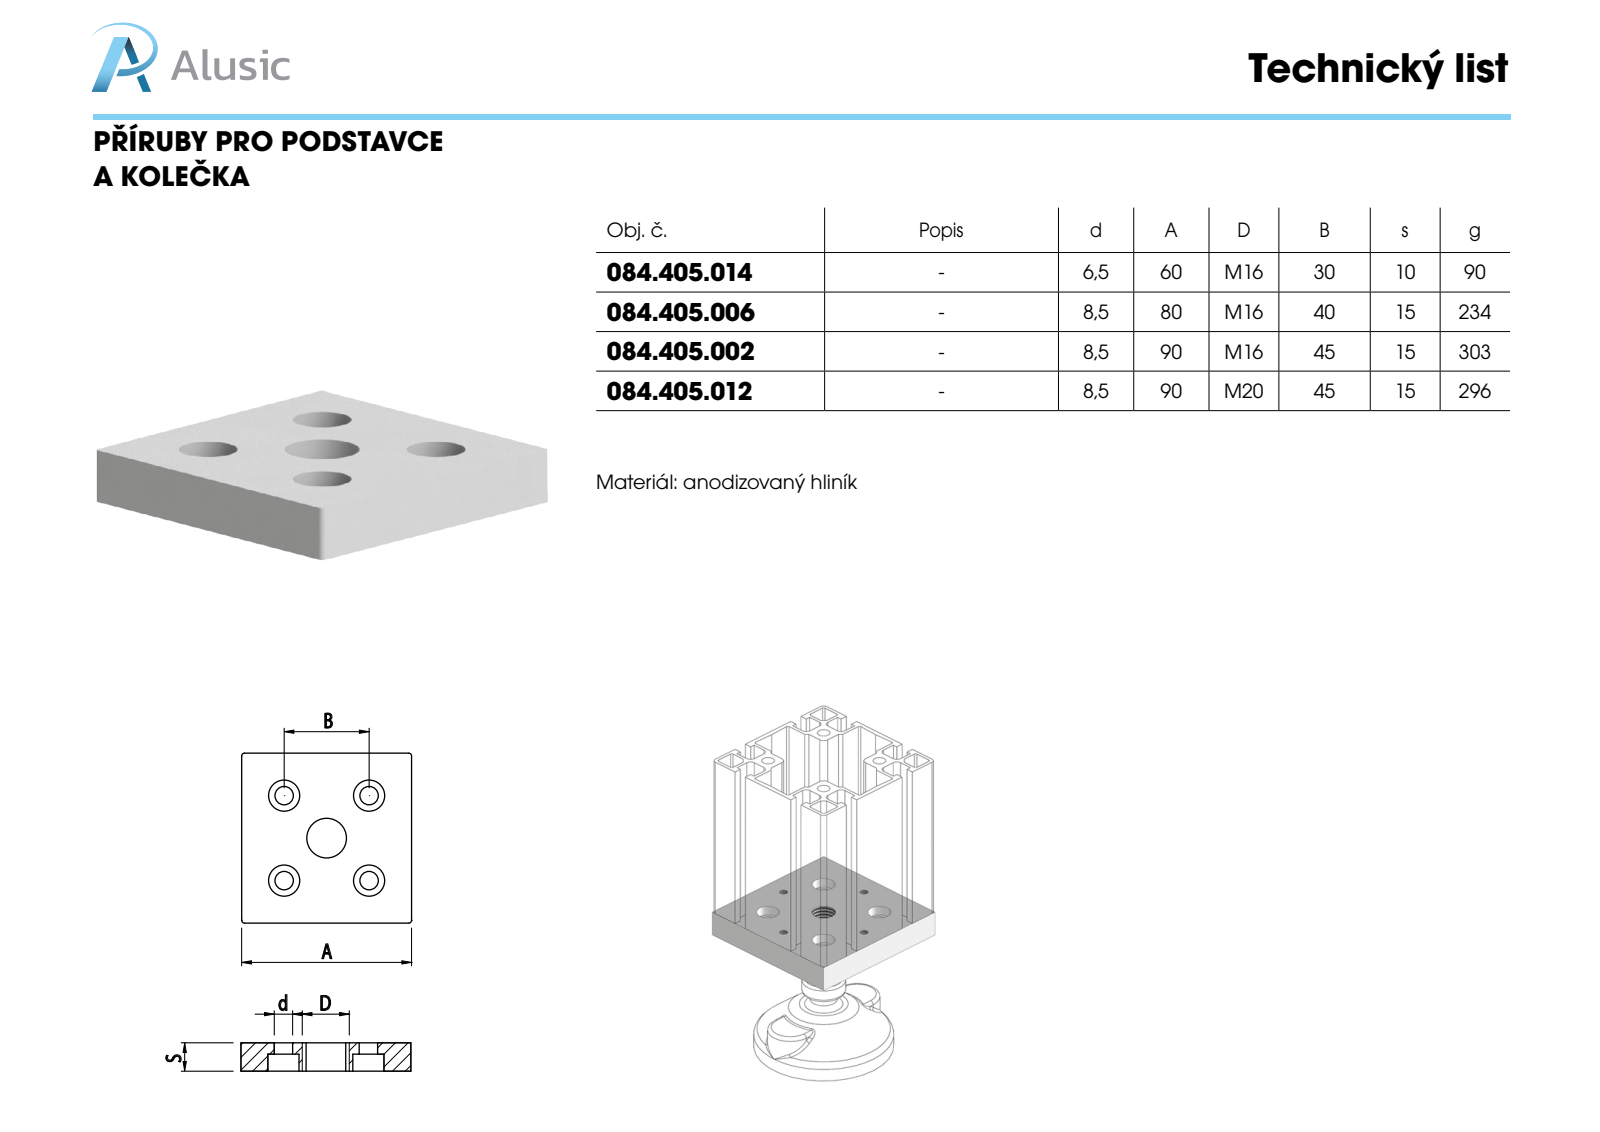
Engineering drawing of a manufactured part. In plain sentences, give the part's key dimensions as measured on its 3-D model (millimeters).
The part is named "084.405.006". Its 3-D file was written by "SolidWorks 2011 (CONFIG_CONTROL_DESIGN)". It is 1 solid with 36 faces: 10 planar, 26 cylindrical and 0 other. Overall it measures 80 by 80 by 15 millimeters. Its volume is 86 239 cubic millimeters and its surface area 20 236 square millimeters. Round holes: 4 of diameter 5, 4 of diameter 9, 4 of diameter 13.5, 1 of diameter 16. The main face-to-face distances are 15, 80, 9.5, 5.5. The hole center spacings are 23.58, 56.18, 28.28, 32.5, 40, 45.96, 56.57, 65.
